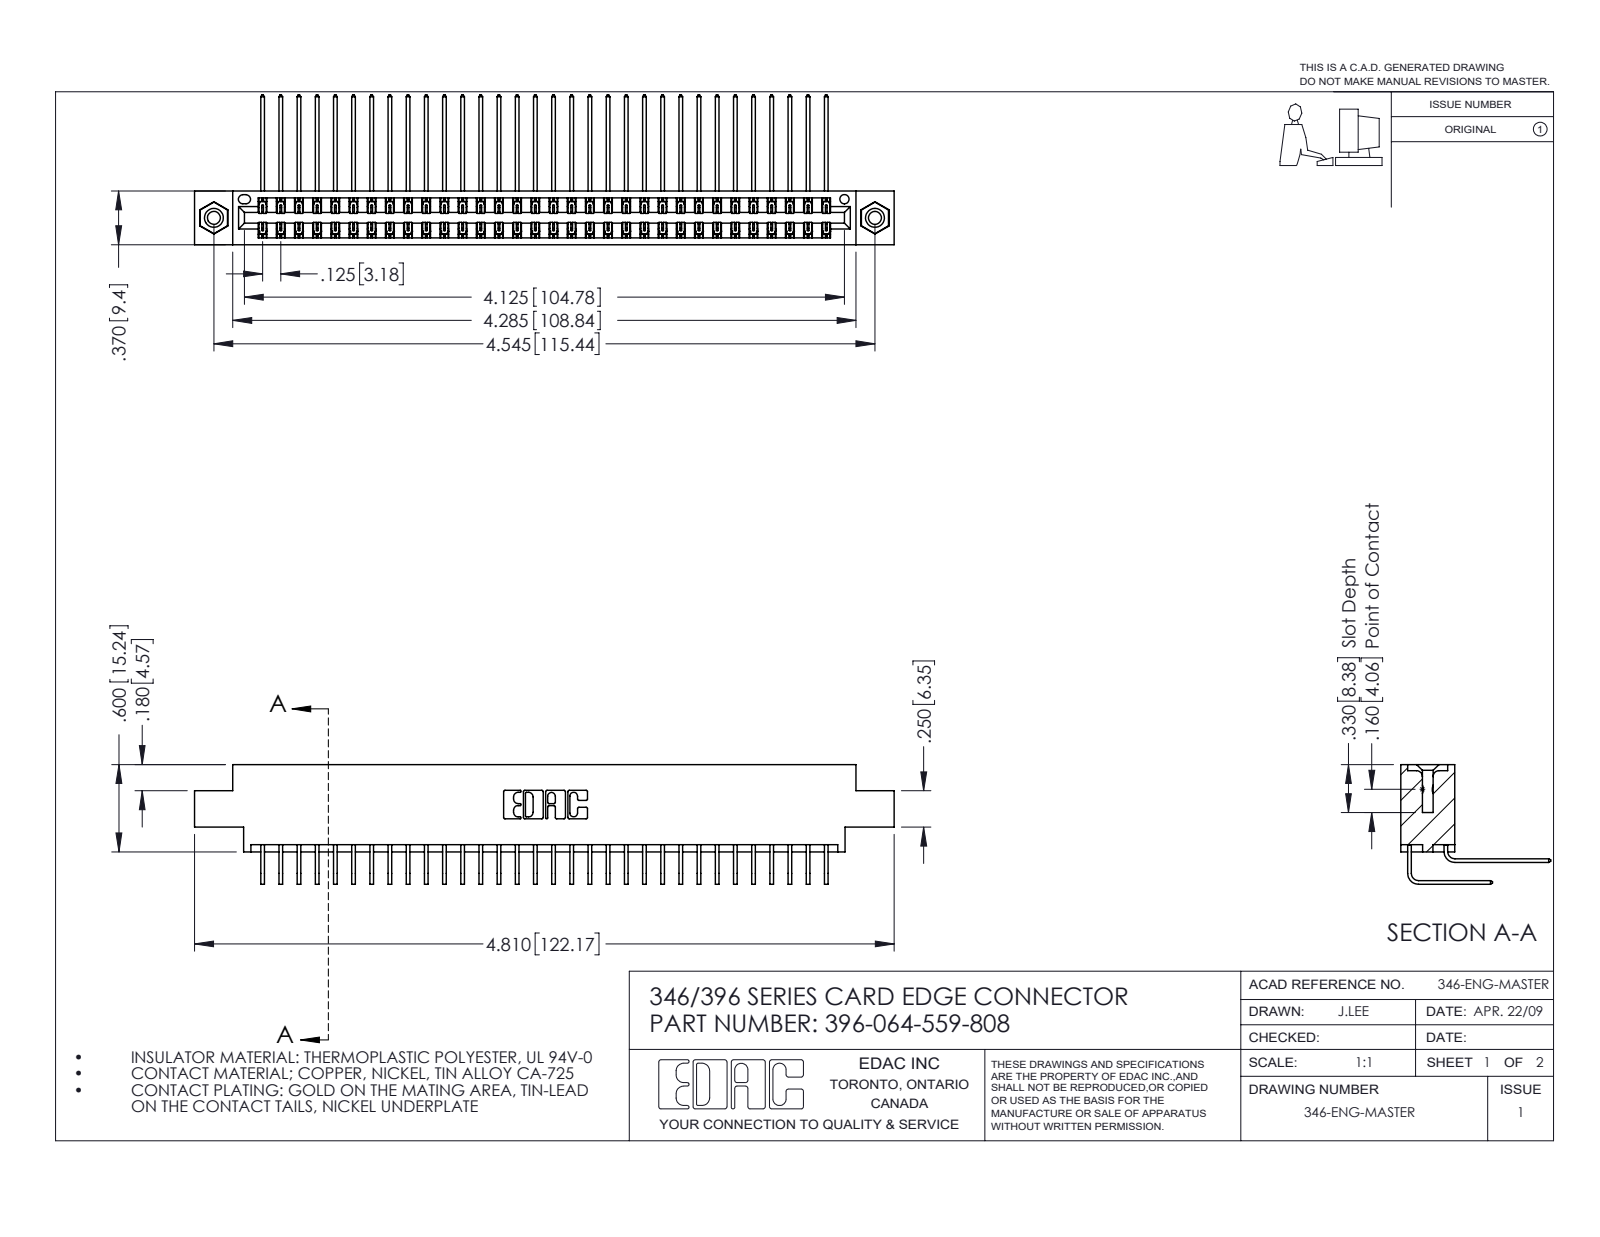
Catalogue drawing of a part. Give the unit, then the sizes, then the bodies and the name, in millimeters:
Units: millimetres
Overall size (bounding box): 122.2 × 26.2 × 20.9
Round holes (diameter × count): ⌀2.3 ×2, ⌀3.2 ×2, ⌀4 ×2, ⌀1.6 ×1
Round bosses / shafts (diameter × count): ⌀3.9 ×2
Partial cylindrical surfaces — rounded edges, fillets, slot ends (radius × count): R0.2 ×96, R0.3 ×22, R0.2 ×6, R0.8 ×6, R0.7 ×3, R0.4 ×2, R0.6 ×2, R0.6 ×2
Main face-to-face distances: 1.2, 8.2, 0.6, 9.4, 6.4, 1.8, 7.6, 7, 5.6, 3.8
Hole centre spacings: 6.2, 110.2, 115.4
Volume: 12 000 mm³ · Surface area: 18 370 mm²
Bodies: 67 solids, 3642 faces (2480 planar, 1146 cylindrical, 16 other)
Part name (STEP PRODUCT): 345-292-001_559 Tail - 2; 345-250-001_345-250-003-102; 345-292-001_558 559 Tail - 1; 346 Part_0.170 Offset - 0.156 Dia-TI (+1 more)
STEP written by: SolidWorks 2016 (CONFIG_CONTROL_DESIGN)
